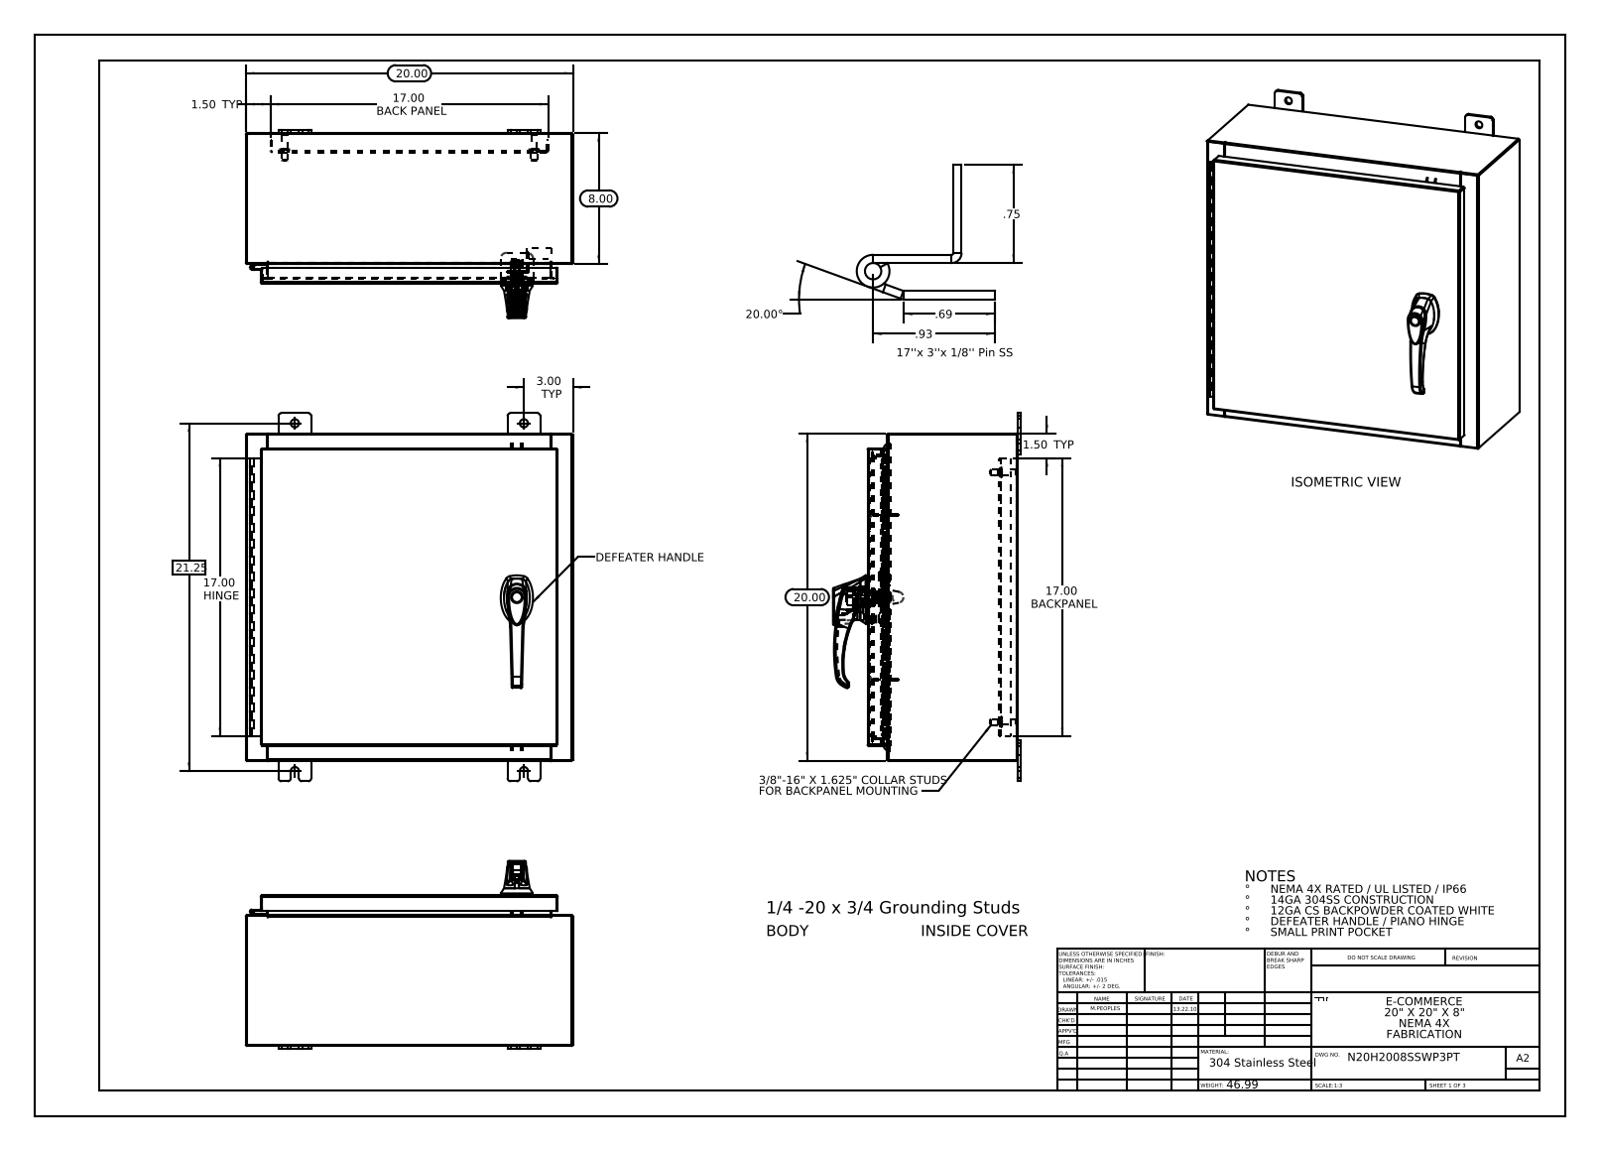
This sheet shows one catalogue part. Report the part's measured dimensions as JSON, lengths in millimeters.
{"part_name": "297026; 2616310101; g26103103_26163303; N20H2008SSWP3PT Body (+8 more)", "step_written_by": "SolidWorks 2013 (CONFIG_CONTROL_DESIGN)", "units": "millimeters", "bodies": {"solids": 31, "faces": 2316, "planar": 817, "cylindrical": 845, "other": 654}, "overall_size": [571.5, 508, 292], "volume_mm3": 2745000, "surface_area_mm2": 2670000, "round_holes": [[12.7, 8], [6.4, 4], [3.5, 3], [4.1, 3], [2, 2], [5.2, 2], [8, 2], [11.1, 2], [3.2, 1], [3.2, 1], [5, 1], [7, 1]], "round_bosses_or_shafts": [[15.9, 4], [9.5, 4], [8.4, 4], [30, 1], [19, 1], [17.3, 1], [16.8, 1], [16.2, 1]], "partial_cylinders_radius": [[3, 37], [0.2, 33], [4.8, 24], [0.3, 22], [2.2, 18], [1, 15], [0.7, 12], [0.2, 6]], "face_to_face_distances": [1.9, 231.8, 506.1, 229.9, 233.7, 504.2, 508, 2.6, 25.4, 27.3], "hole_center_spacings": [86.5, 7.5, 15.9, 21.4, 31.8, 33.4, 39.6, 47.2]}
